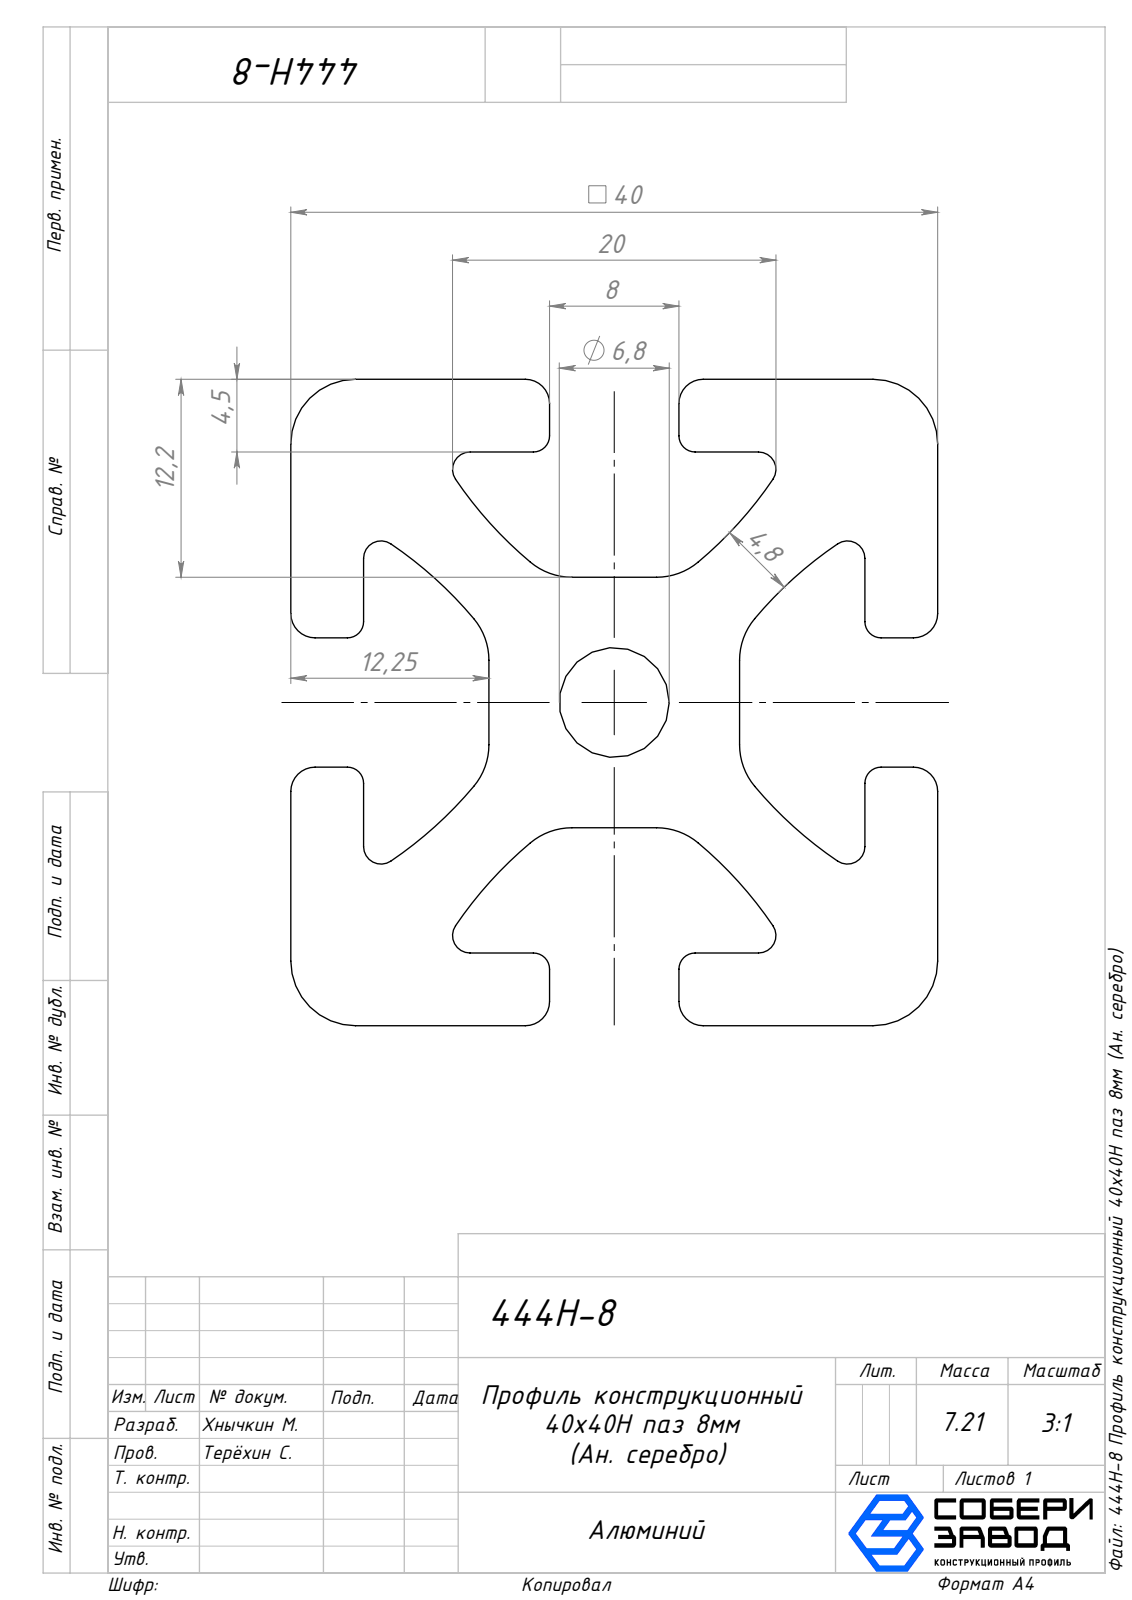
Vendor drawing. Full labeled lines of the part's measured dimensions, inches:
Part name (STEP PRODUCT): V053-8952
STEP written by: SolidWorks 2025 (AUTOMOTIVE_DESIGN)
Units: inches
Bodies: 1 solid, 78 faces (30 planar, 48 cylindrical, 0 other)
Overall size (bounding box): 39.37 × 1.575 × 1.575
Volume: 56.05 in³ · Surface area: 509.2 in²
Round holes (diameter × count): ⌀0.268 ×1
Partial cylindrical surfaces — rounded edges, fillets, slot ends (radius × count): R0.157 ×12, R0.039 ×8, R0.043 ×8, R0.059 ×8, R0.984 ×8
Main face-to-face distances: 1.575, 0.177, 1.398, 0.482, 1.093, 0.305, 0.915, 0.63, 0.945, 0.453
